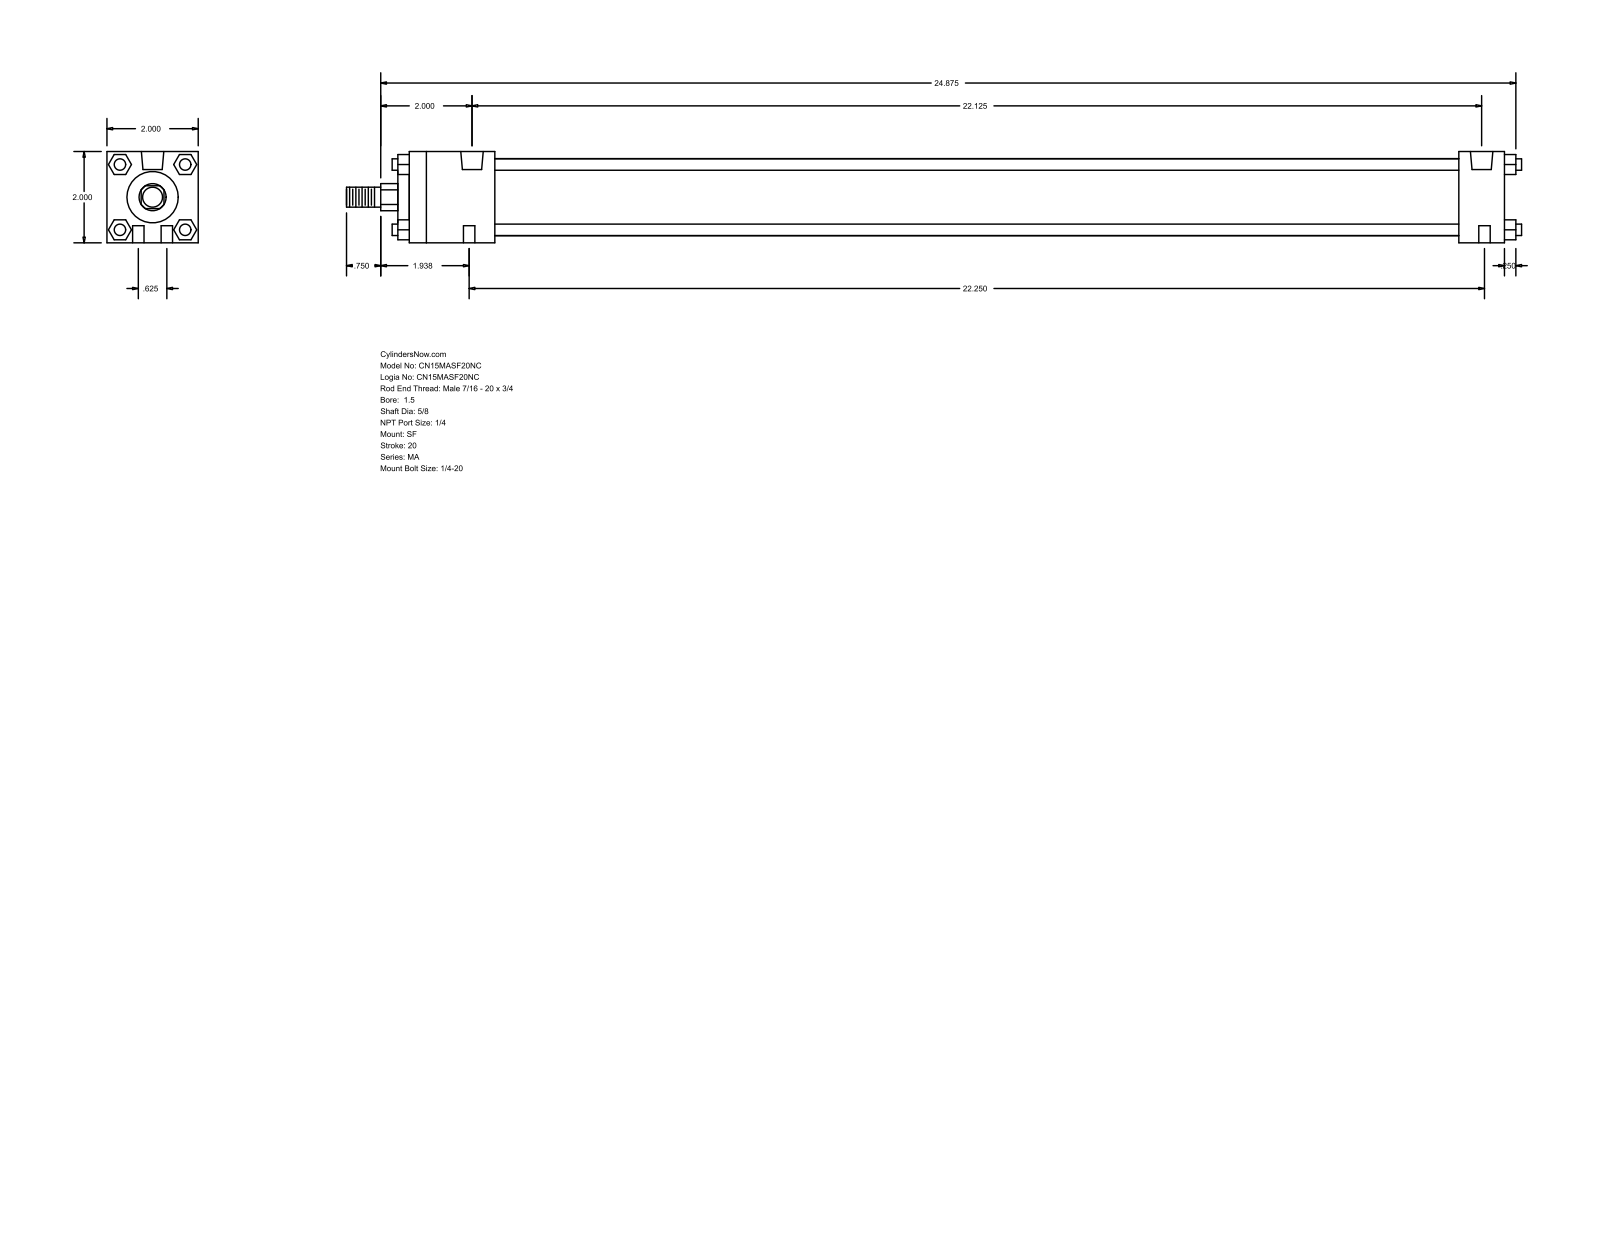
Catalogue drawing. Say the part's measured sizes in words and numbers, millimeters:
The part is named "MA_SF__0150_0.625". Its 3-D file was written by "GSSL Pune (CONFIG_CONTROL_DESIGN)". It is 0 solids with 124 faces: 94 planar, 30 cylindrical and 0 other. Overall it measures 654.05 by 50.8 by 50.8 millimeters. Round holes: 4 of diameter 6.35, 2 of diameter 7.94, 2 of diameter 12.49. Round bosses or shafts: 4 of diameter 6.35, 1 of diameter 42.93, 1 of diameter 28.57, 1 of diameter 15.88, 1 of diameter 11.11. Partial cylindrical surfaces (rounded edges, fillets, slot ends): 1 of radius 7.54. The main face-to-face distances are 50.8, 609.6, 6.35, 25.4, 615.95, 47.62, 584.2, 536.58, 561.98, 53.97. The hole center spacings are 8.1, 563.62, 15.88, 561.97, 565.15, 565.37.
